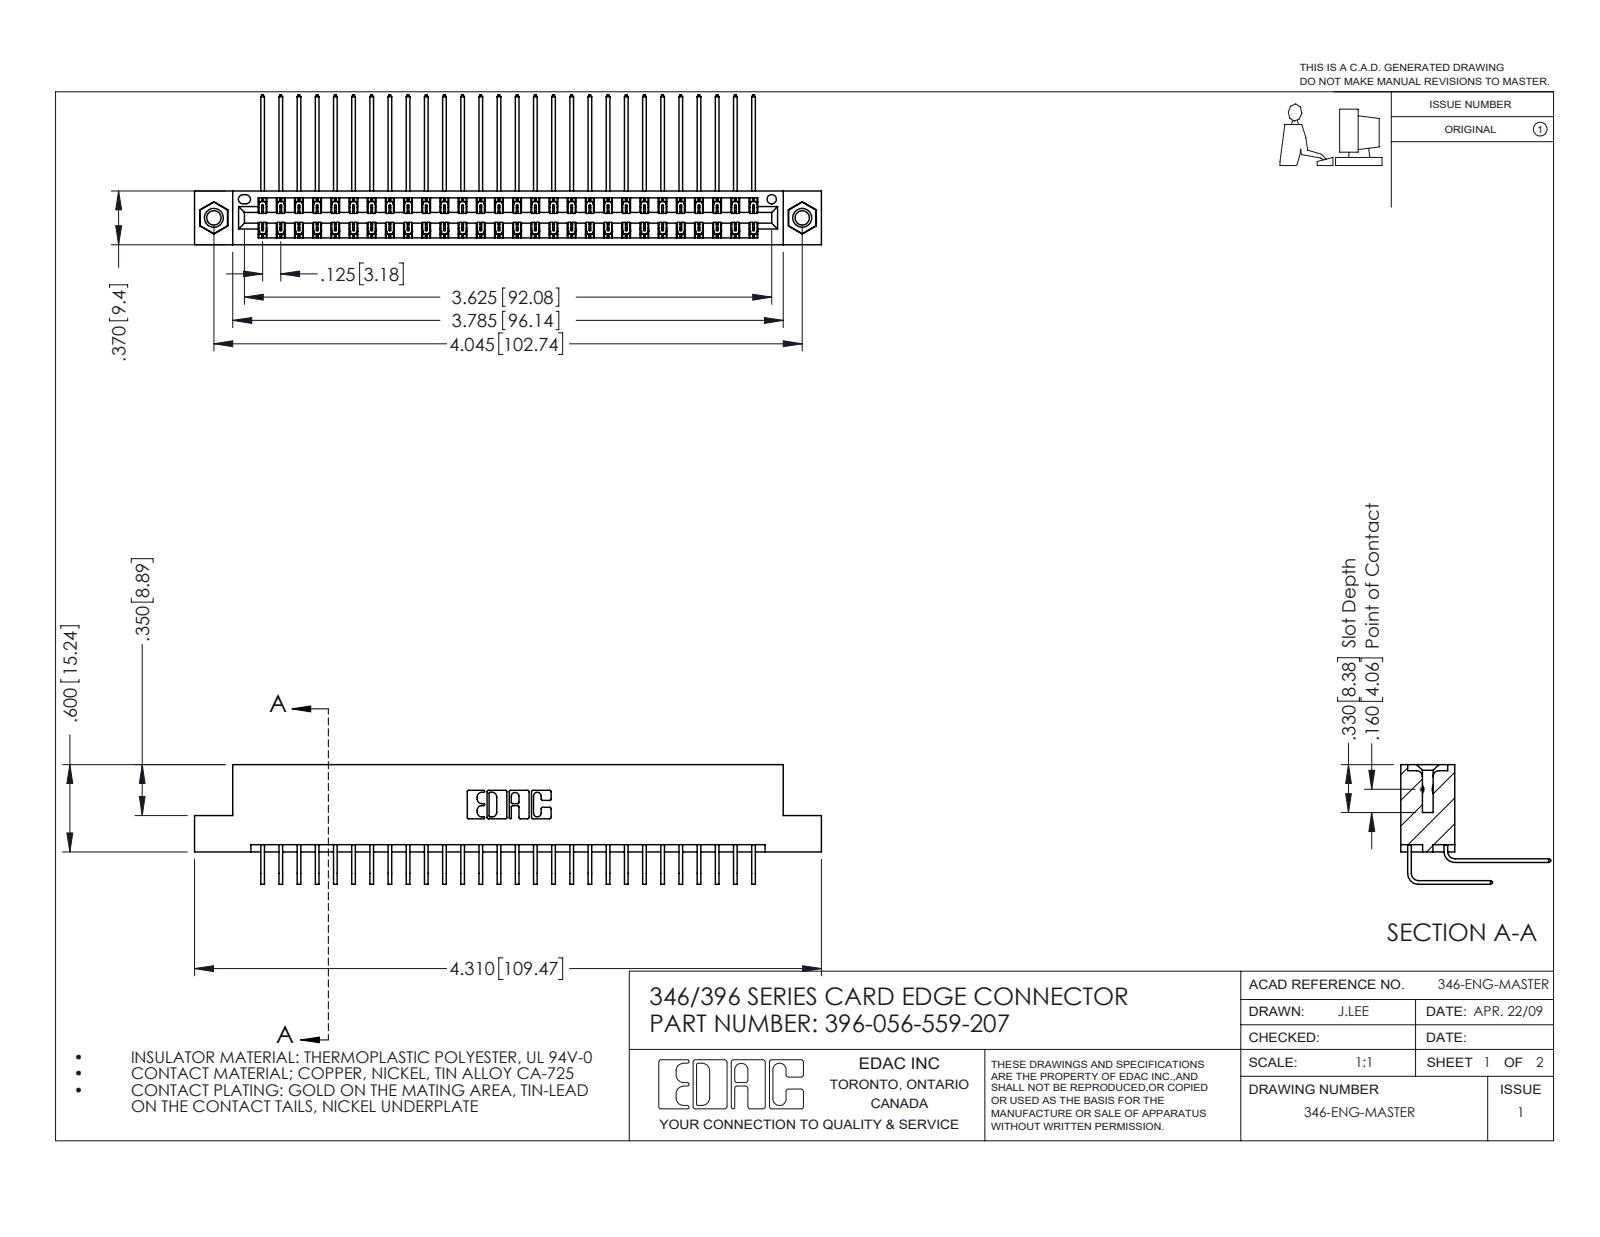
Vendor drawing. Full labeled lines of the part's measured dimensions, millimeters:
Part name (STEP PRODUCT): 345-292-001_558 559 Tail - 1; 346 Part_Flush Mounting Lugs - 0.156 Dia-TI; 396-056-559-207; 345-292-001_559 Tail - 2 (+1 more)
STEP written by: SolidWorks 2016 (CONFIG_CONTROL_DESIGN)
Units: millimetres
Bodies: 59 solids, 3206 faces (2180 planar, 1010 cylindrical, 16 other)
Overall size (bounding box): 109.5 × 26.2 × 20.9
Volume: 10 900 mm³ · Surface area: 16 320 mm²
Round holes (diameter × count): ⌀2.5 ×2, ⌀3.2 ×2, ⌀4 ×2, ⌀1.6 ×1
Round bosses / shafts (diameter × count): ⌀3.9 ×2
Partial cylindrical surfaces — rounded edges, fillets, slot ends (radius × count): R0.2 ×84, R0.3 ×22, R0.2 ×6, R0.8 ×6, R0.7 ×3, R0.4 ×2, R0.6 ×2, R0.6 ×2
Main face-to-face distances: 1.2, 8.2, 0.6, 9.4, 6.4, 1.8, 7.6, 7, 3.8, 5.6
Hole centre spacings: 6.2, 97.5, 102.7
